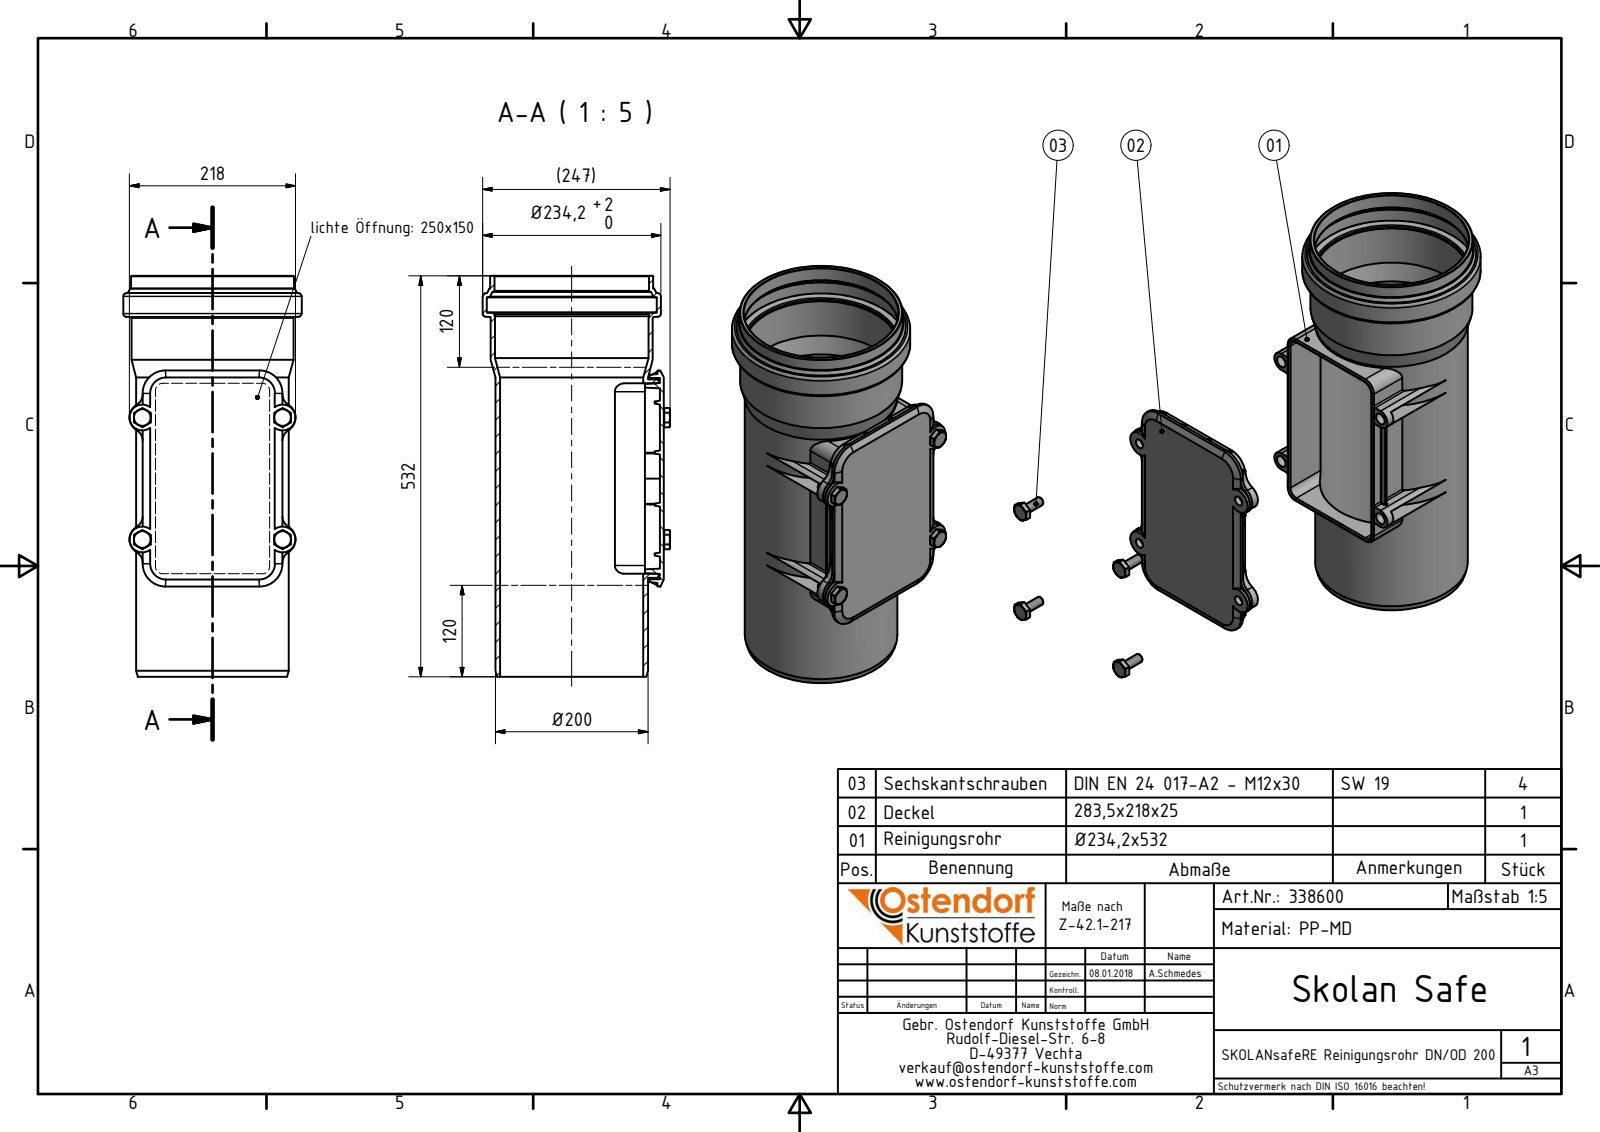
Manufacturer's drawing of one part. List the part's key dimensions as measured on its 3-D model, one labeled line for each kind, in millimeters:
Part name (STEP PRODUCT): 338600 SKRE Reinigungsrohr DN_OD 200; 338600 SKRE Reinigungsrohr DN_OD 200 Deckel; DIN 6914 - M12 x 30; 338600 SKOLANsafeRE Reinigungsrohr DN_OD 200
STEP written by: Autodesk Inventor 2016 (AUTOMOTIVE_DESIGN)
Units: millimetres
Bodies: 6 solids, 593 faces (348 planar, 121 cylindrical, 124 other)
Overall size (bounding box): 526 × 246.1 × 234.2
Volume: 2 532 000 mm³ · Surface area: 897 074 mm²
Round holes (diameter × count): ⌀13 ×4, ⌀16 ×4, ⌀187.9 ×1, ⌀201.5 ×1, ⌀202.7 ×1, ⌀223 ×1
Round bosses / shafts (diameter × count): ⌀20 ×4, ⌀12 ×4, ⌀234.2 ×1, ⌀213.9 ×1, ⌀212.7 ×1, ⌀200.3 ×1
Partial cylindrical surfaces — rounded edges, fillets, slot ends (radius × count): R1 ×16, R20 ×12, R2 ×8, R4 ×8, R15 ×8, R10.95 ×4, R13 ×4, R13.8 ×4
Main face-to-face distances: 5.3, 5.1, 155.1, 150, 160.2, 16.5, 160, 8.5, 3.2, 47.56
Hole centre spacings: 160, 184, 243.84
